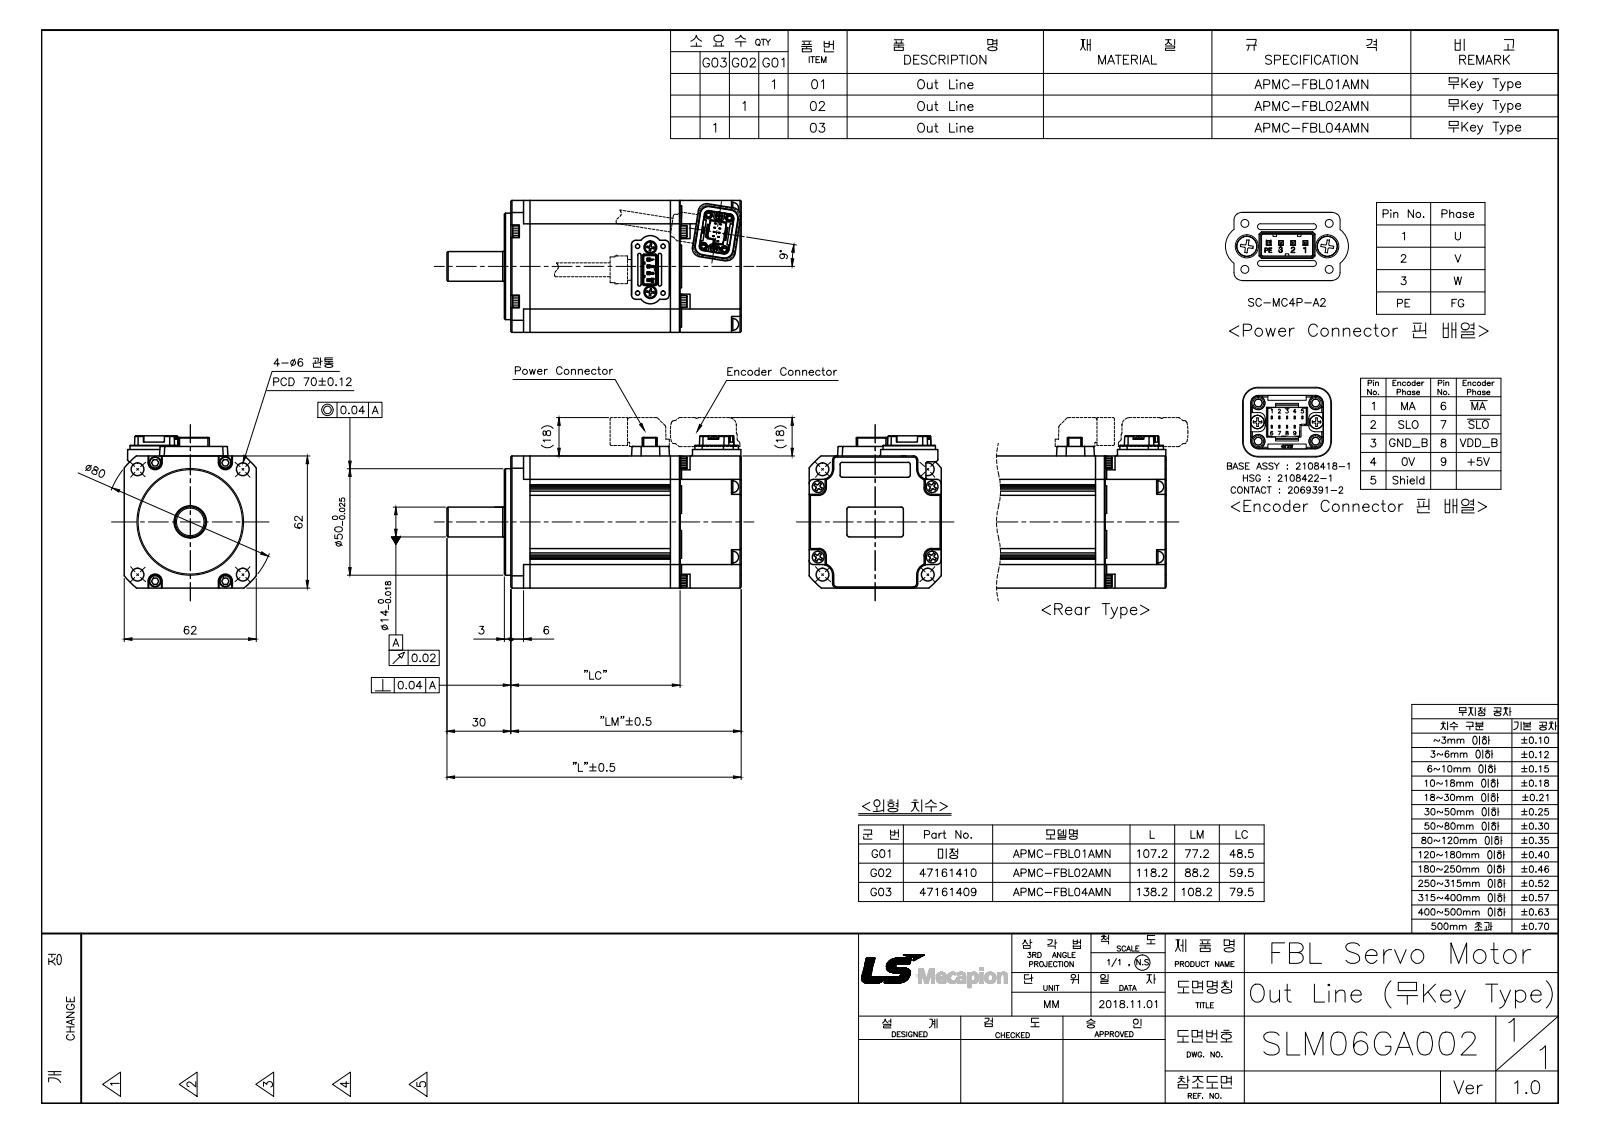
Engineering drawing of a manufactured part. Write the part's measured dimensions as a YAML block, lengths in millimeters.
part_name: "SLM06GA002G02_Out Line(APMC-FBL02AMN)"
step_written_by: "SolidWorks 2011 (AUTOMOTIVE_DESIGN)"
units: millimeters
bodies: {solids: 44, faces: 1807, planar: 1154, cylindrical: 465, other: 188}
overall_size: [118.2, 71.5, 62]
volume: 312491
surface_area: 70461
round_holes:
  - {diameter: 2.1, count: 10}
  - {diameter: 3, count: 10}
  - {diameter: 3.5, count: 8}
  - {diameter: 6, count: 6}
  - {diameter: 3.1, count: 4}
  - {diameter: 2, count: 2}
  - {diameter: 3.3, count: 1}
  - {diameter: 3.4, count: 1}
  - {diameter: 15.3, count: 1}
round_bosses_or_shafts:
  - {diameter: 5.4, count: 6}
  - {diameter: 5.6, count: 4}
  - {diameter: 5.5, count: 4}
  - {diameter: 2.2, count: 2}
  - {diameter: 50, count: 1}
  - {diameter: 15, count: 1}
  - {diameter: 14.8, count: 1}
  - {diameter: 14, count: 1}
partial_cylinders:
  - {radius: 0.2, count: 20}
  - {radius: 0.3, count: 20}
  - {radius: 1, count: 12}
  - {radius: 0.15, count: 9}
  - {radius: 2, count: 8}
  - {radius: 3, count: 8}
  - {radius: 0.45, count: 7}
  - {radius: 0.11, count: 6}
face_to_face_distances: [4.5, 0.7, 46, 50.5, 5.2, 51.2, 62, 3, 28.7, 51]
hole_center_spacings: [44.75, 6.02, 8.5, 8.8, 15.29, 16.01, 22.32, 31.47]
